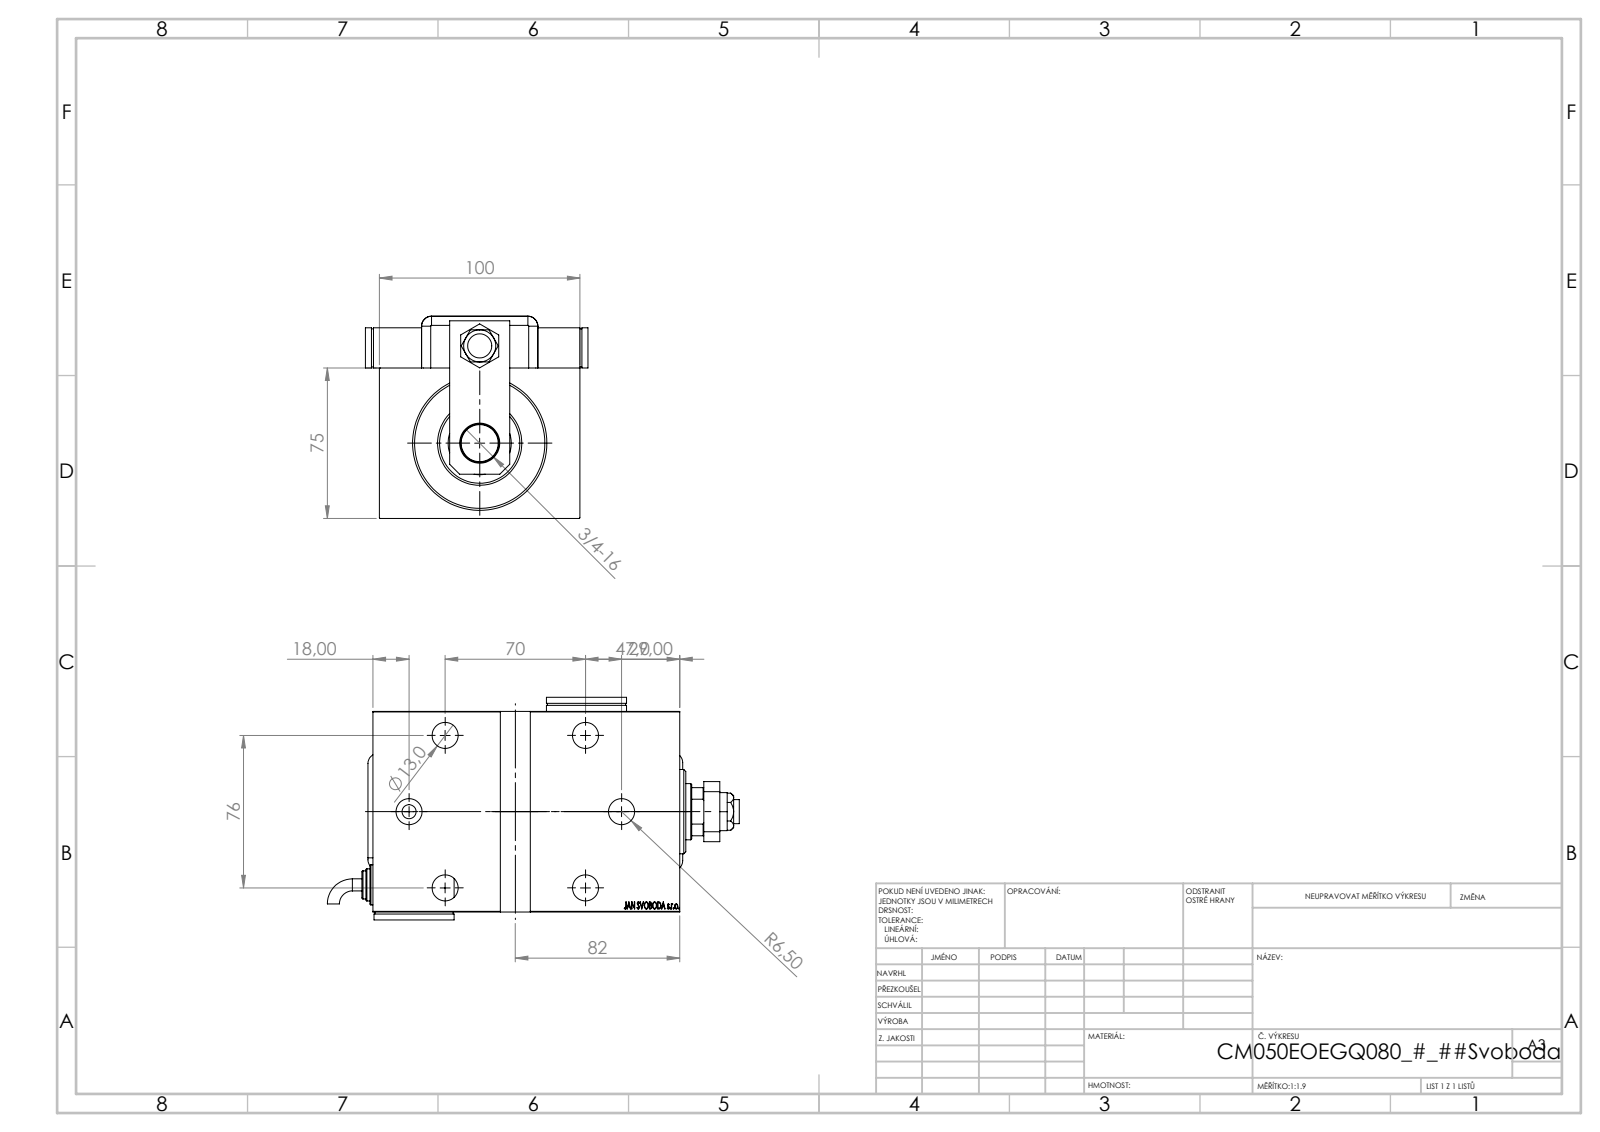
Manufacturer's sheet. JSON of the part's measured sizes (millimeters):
{"part_name": "ZARAZKA_Q; NUT_D19; KRYT; NUT_D13 (+7 more)", "step_written_by": "SolidWorks 2019 (CONFIG_CONTROL_DESIGN)", "units": "millimeters", "bodies": {"solids": 13, "faces": 1233, "planar": 615, "cylindrical": 101, "other": 517}, "overall_size": [205.46, 111, 100.8], "volume_mm3": 1156000, "surface_area_mm2": 204526, "round_holes": [[13, 7], [19, 4], [4, 2], [8, 2], [12, 1], [14, 1], [18.5, 1], [20, 1], [28, 1], [31.5, 1], [50, 1], [65, 1]], "round_bosses_or_shafts": [[20, 3], [16, 2], [14, 2], [6, 2], [52, 1], [42, 1], [7, 1]], "partial_cylinders_radius": [[5, 9], [10, 1], [13.5, 1]], "face_to_face_distances": [3, 75, 100, 100.8, 25.8, 153, 22.8, 97.8, 14, 20], "hole_center_spacings": [42.05, 95.85, 22.36, 47.2, 61.22, 70, 76, 103.32]}
